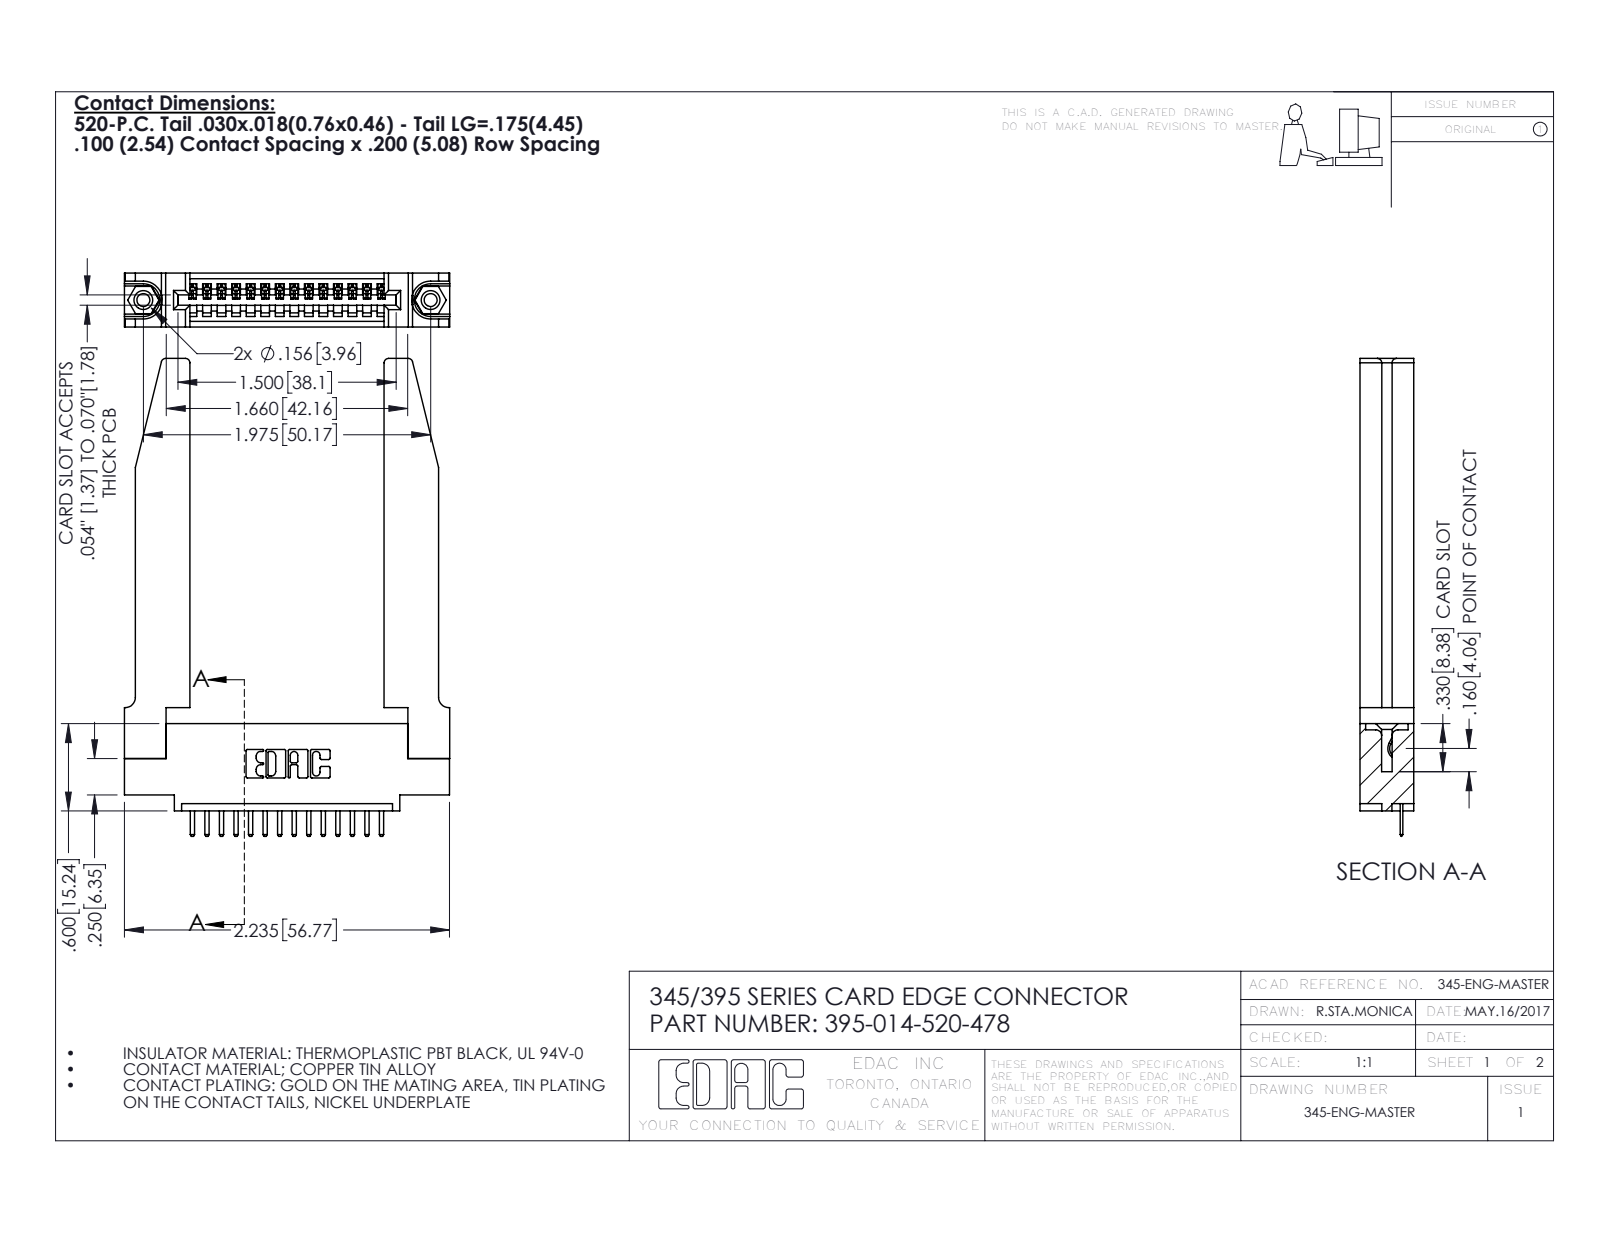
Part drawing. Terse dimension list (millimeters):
name: 395-014-520-478; 345 Part_0.110 Offset - 0.156 Dia-TH; 345-292-001_345-293-120; 345-250-001_345-250-001-102 (+1 more)
written by: SolidWorks 2016 (CONFIG_CONTROL_DESIGN)
unit: mm
bodies: 19 solids, 1232 faces (814 planar, 366 cylindrical, 52 other)
size: 83.4 × 56.8 × 9.4
volume: 12 800 mm³; area: 13 130 mm²
holes: 2× ⌀2.3, 2× ⌀3.2, 2× ⌀4, 1× ⌀1.6
bosses: 2× ⌀3.9
rounds: 30× R0.3, 28× R0.2, 22× R0.3, 8× R0.8, 6× R0.2, 6× R0.8, 3× R0.7, 2× R0.8
face distances: 9.4, 1.8, 7.6, 3.8, 3.8, 5.6, 2, 33.9, 5.1, 2.5
hole spacings: 6.9, 44.2, 50.2
